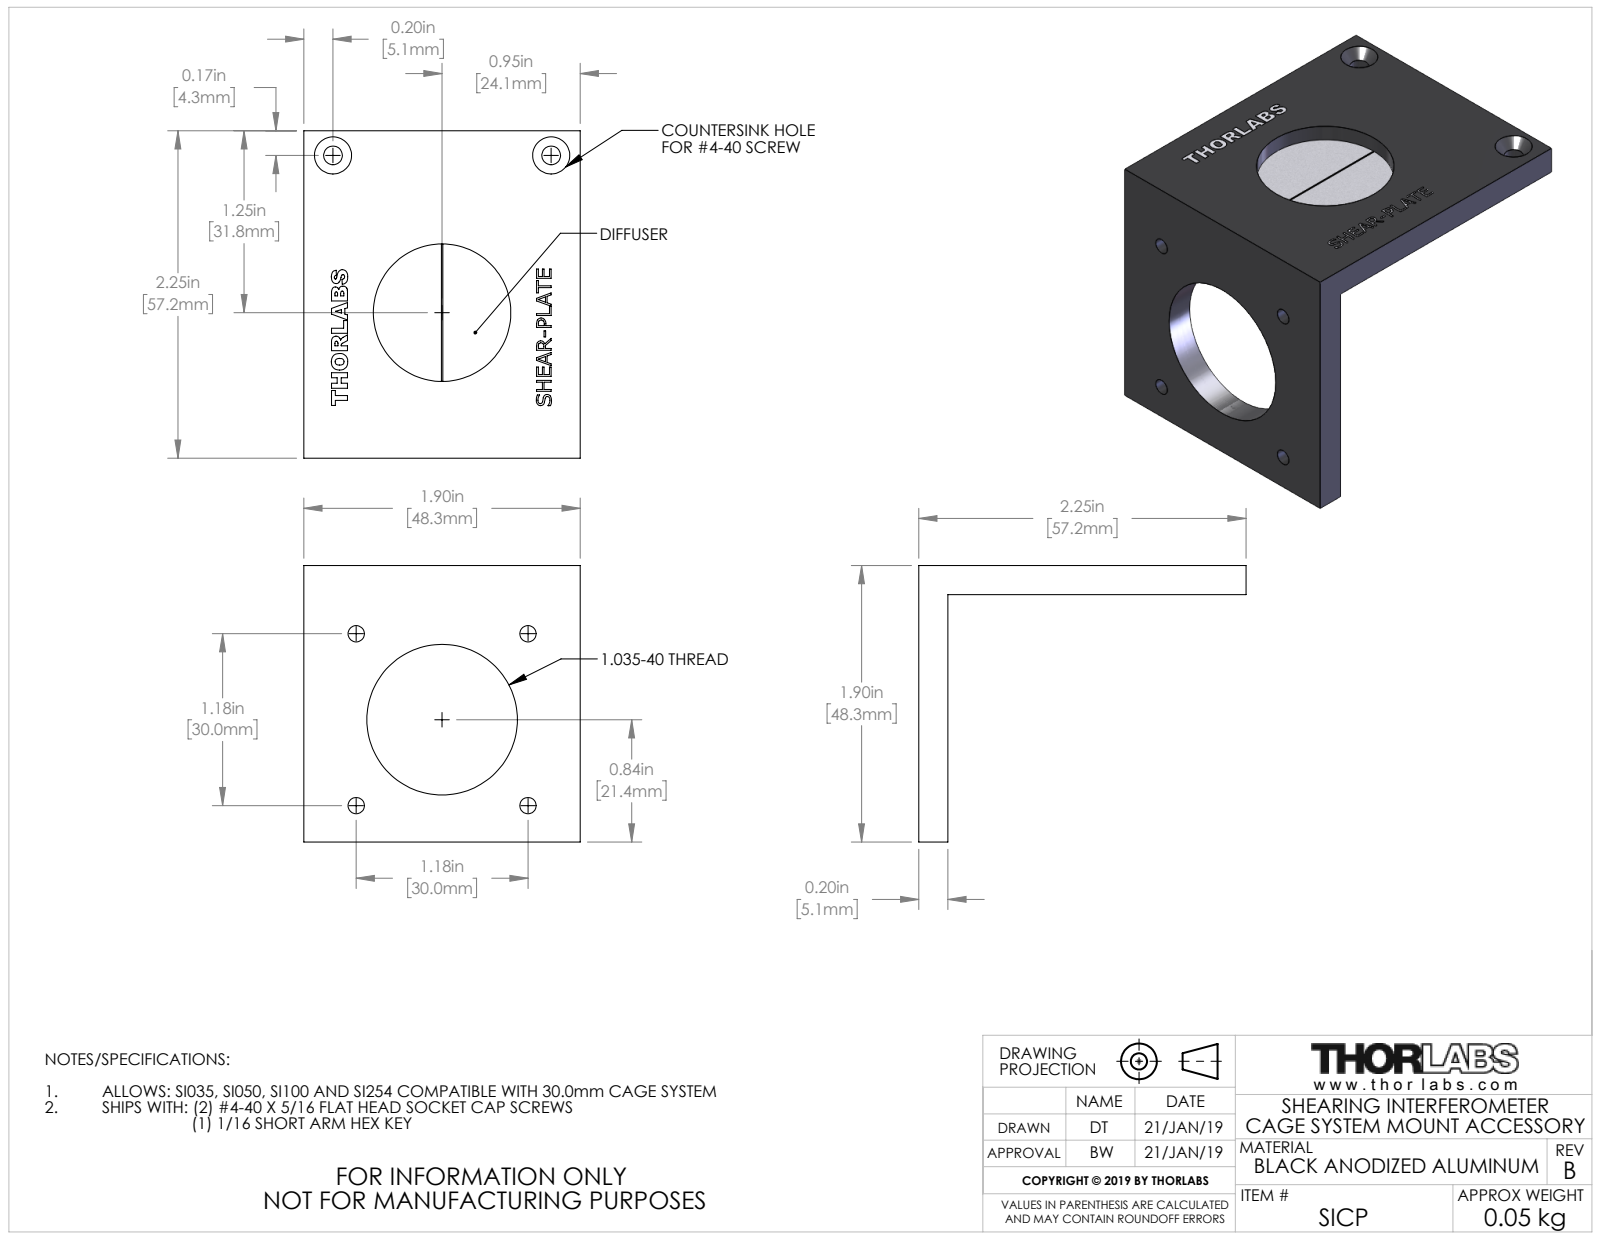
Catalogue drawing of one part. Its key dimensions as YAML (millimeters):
part_name: "TTN015344-E0W"
step_written_by: "SolidWorks 2018 (CONFIG_CONTROL_DESIGN)"
units: millimeters
bodies: {solids: 2, faces: 67, planar: 43, cylindrical: 20, other: 4}
overall_size: [57.2, 48.3, 48.3]
volume: 20170
surface_area: 11380
round_holes:
  - {diameter: 2.8, count: 4}
  - {diameter: 3.3, count: 2}
  - {diameter: 24, count: 1}
  - {diameter: 25.5, count: 1}
  - {diameter: 26.3, count: 1}
round_bosses_or_shafts:
  - {diameter: 25.4, count: 1}
face_to_face_distances: [5.1, 48.3, 2.2, 2.9, 2, 4.9, 43.2, 43.4, 45.4, 52.1]
hole_center_spacings: [21.2, 30, 33.4, 42.4, 38.1]
